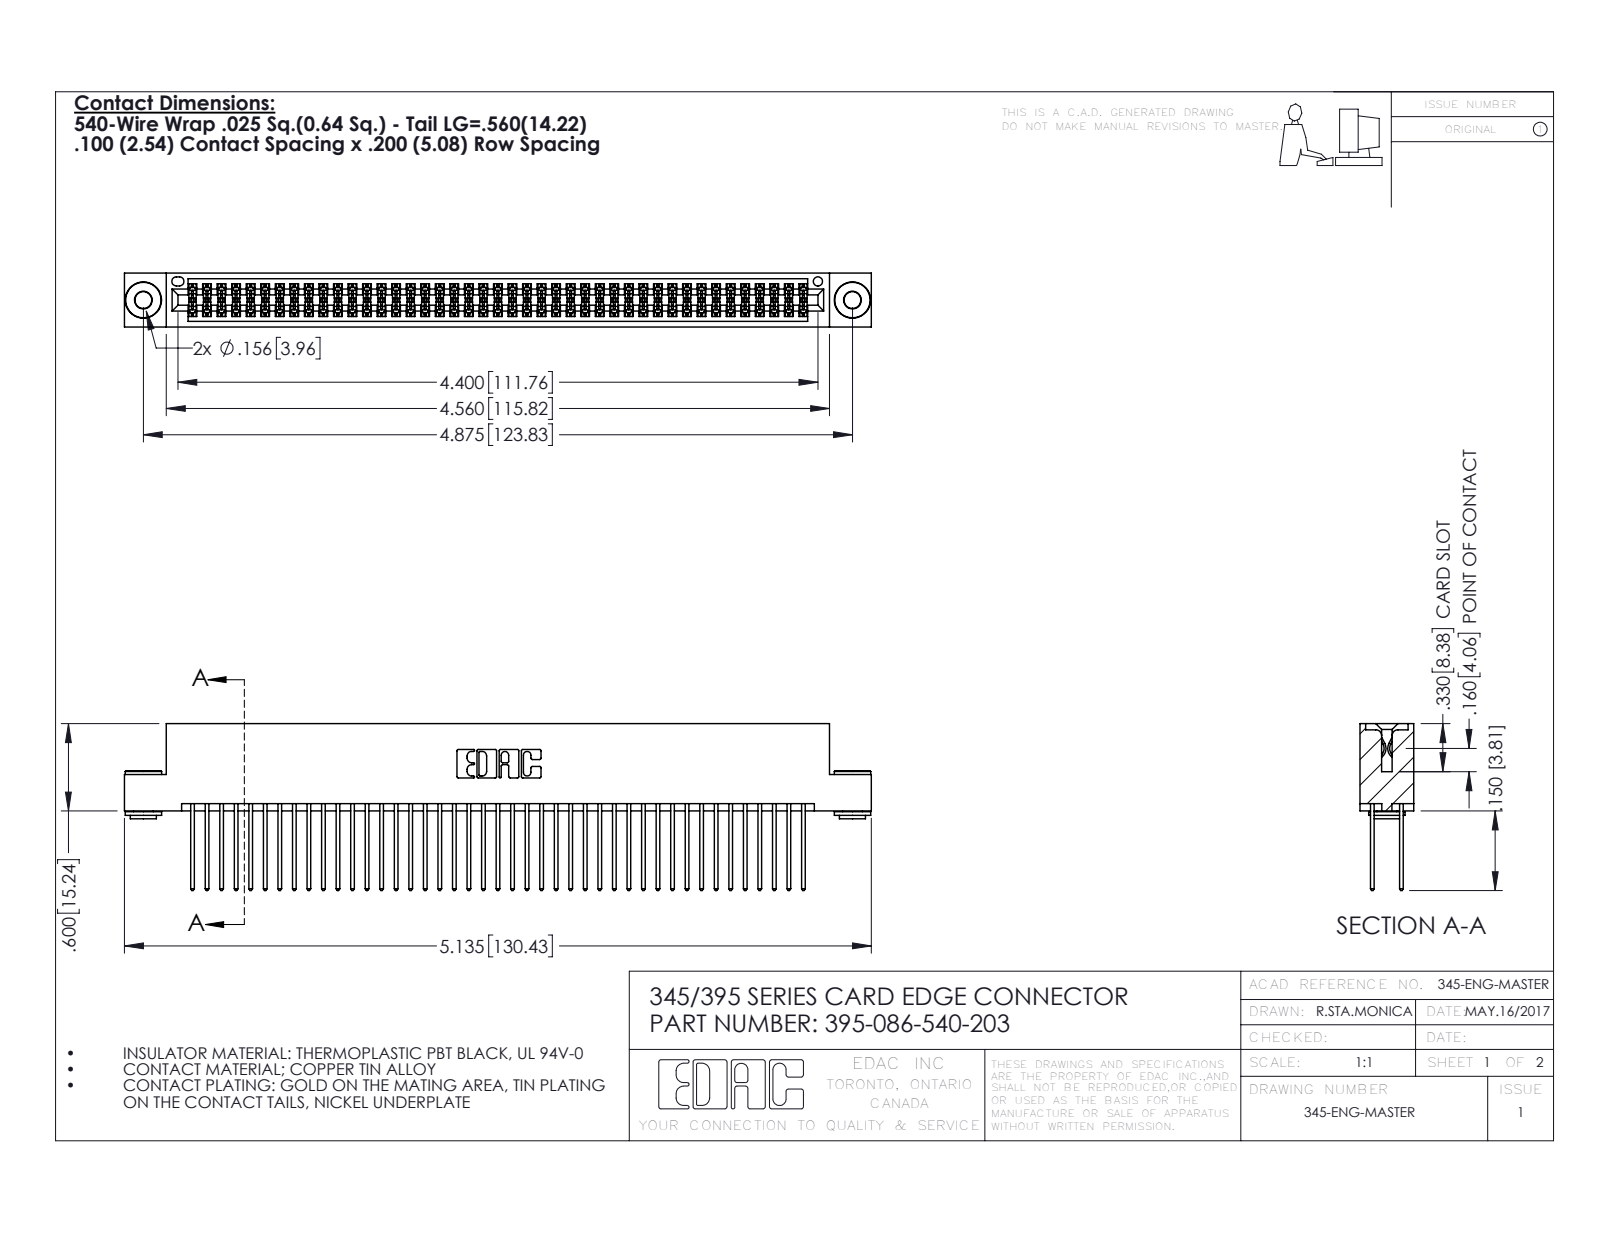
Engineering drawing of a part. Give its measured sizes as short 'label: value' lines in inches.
name: 395-086-540-203; 345-250-002_345-250-002-102; 345 Part_Flush Mounting Lugs - 0.156 Dia-TH; 345-292-001_345-293-140
written by: SolidWorks 2016 (CONFIG_CONTROL_DESIGN)
unit: in
bodies: 89 solids, 4464 faces (2928 planar, 1528 cylindrical, 8 other)
size: 5.135 × 1.147 × 0.37
volume: 0.795 in³; area: 32.53 in²
holes: 2× ⌀0.116, 2× ⌀0.156, 1× ⌀0.064
bosses: 2× ⌀0.25, 2× ⌀0.18, 2× ⌀0.136
rounds: 129× R0.006, 86× R0.01, 22× R0.01, 6× R0.007, 6× R0.031, 3× R0.026, 2× R0.014, 2× R0.019
face distances: 0.072, 0.298, 0.2, 0.025, 0.098, 0.272, 0.37, 0.225, 0.175, 0.149
hole spacings: 0.27, 4.639, 4.875
